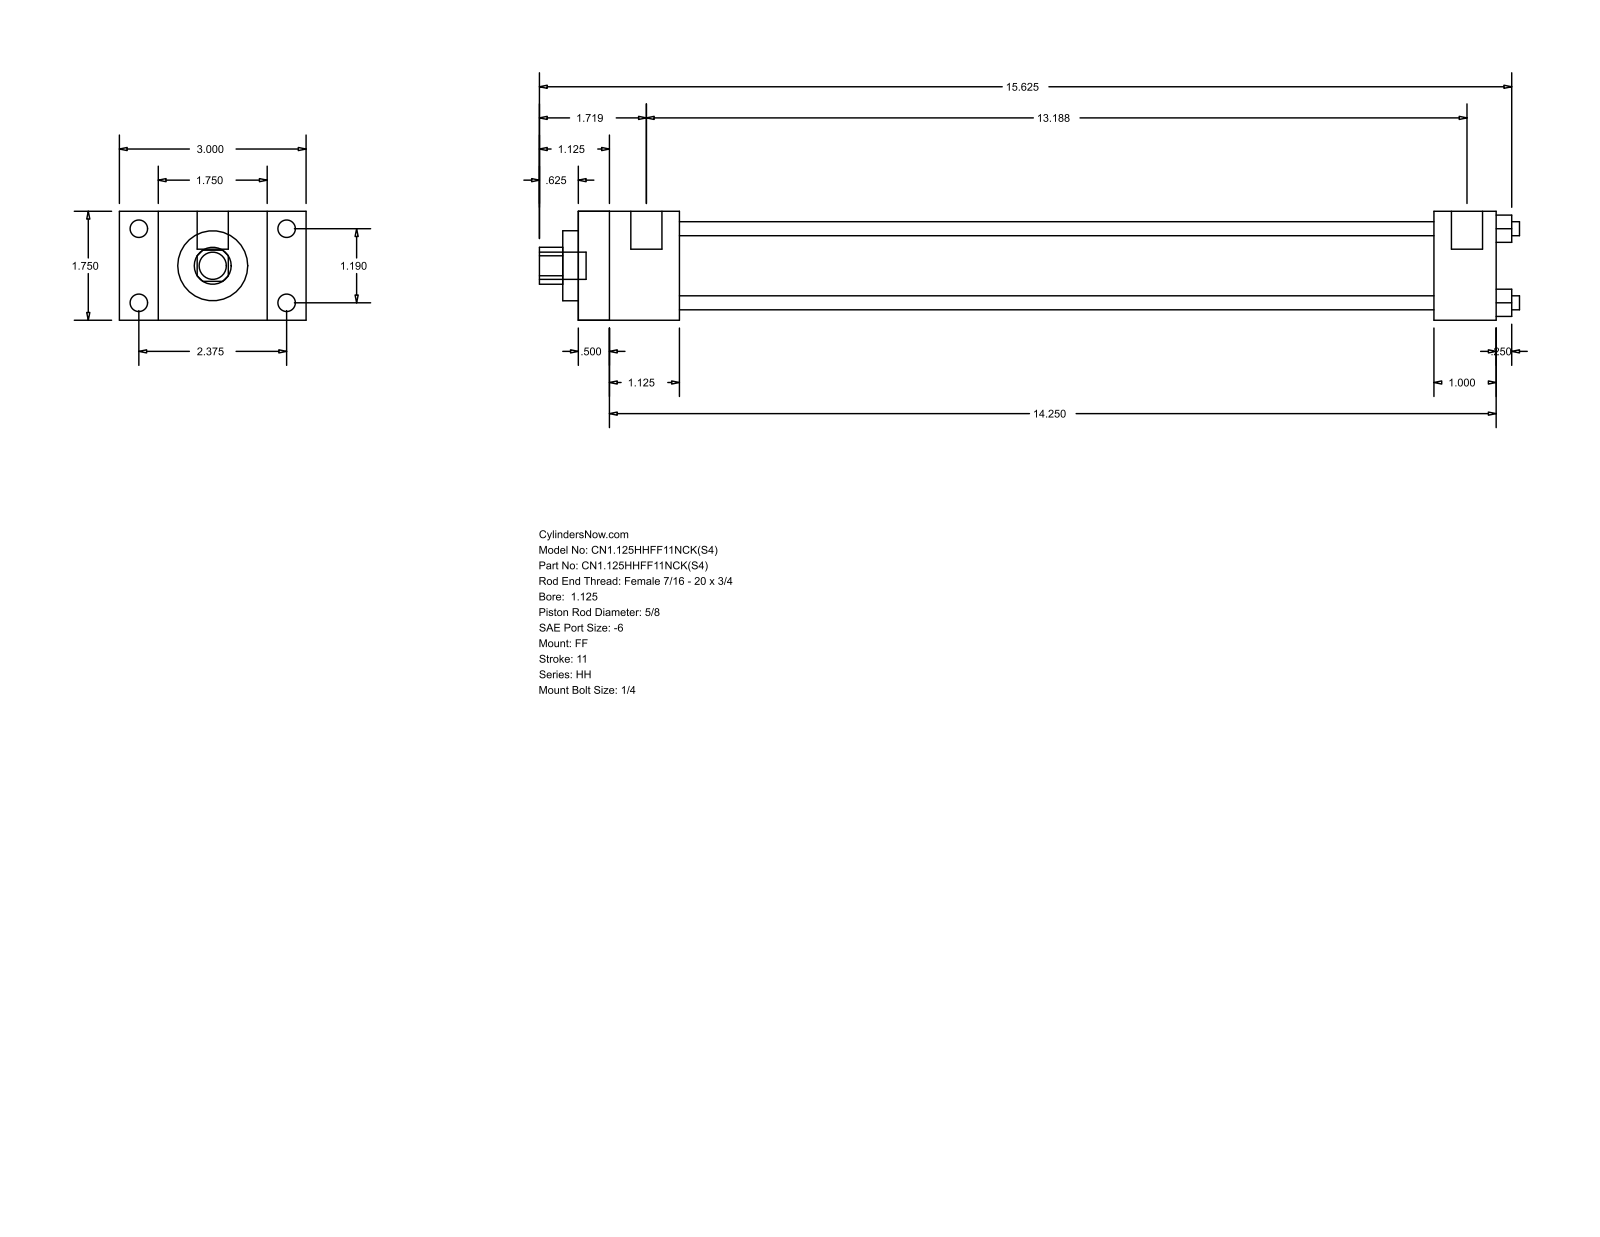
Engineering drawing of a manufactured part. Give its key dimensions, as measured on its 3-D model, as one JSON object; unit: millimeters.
{"part_name": "HH_FF__0112_0.625", "step_written_by": "GSSL Pune (CONFIG_CONTROL_DESIGN)", "units": "millimeters", "bodies": {"solids": 0, "faces": 92, "planar": 64, "cylindrical": 28, "other": 0}, "overall_size": [400.05, 76.2, 44.45], "round_holes": [[5.71, 4], [15.88, 1], [28.57, 1], [34.92, 1]], "round_bosses_or_shafts": [[7.14, 4], [5.56, 4], [12.7, 2], [11.11, 1]], "partial_cylinders_radius": [[7.54, 1]], "face_to_face_distances": [44.46, 374.64, 15.87, 12.69, 361.95, 60.33, 28.58, 41.27, 349.24, 336.55], "hole_center_spacings": [21.37, 30.22, 42.74]}
